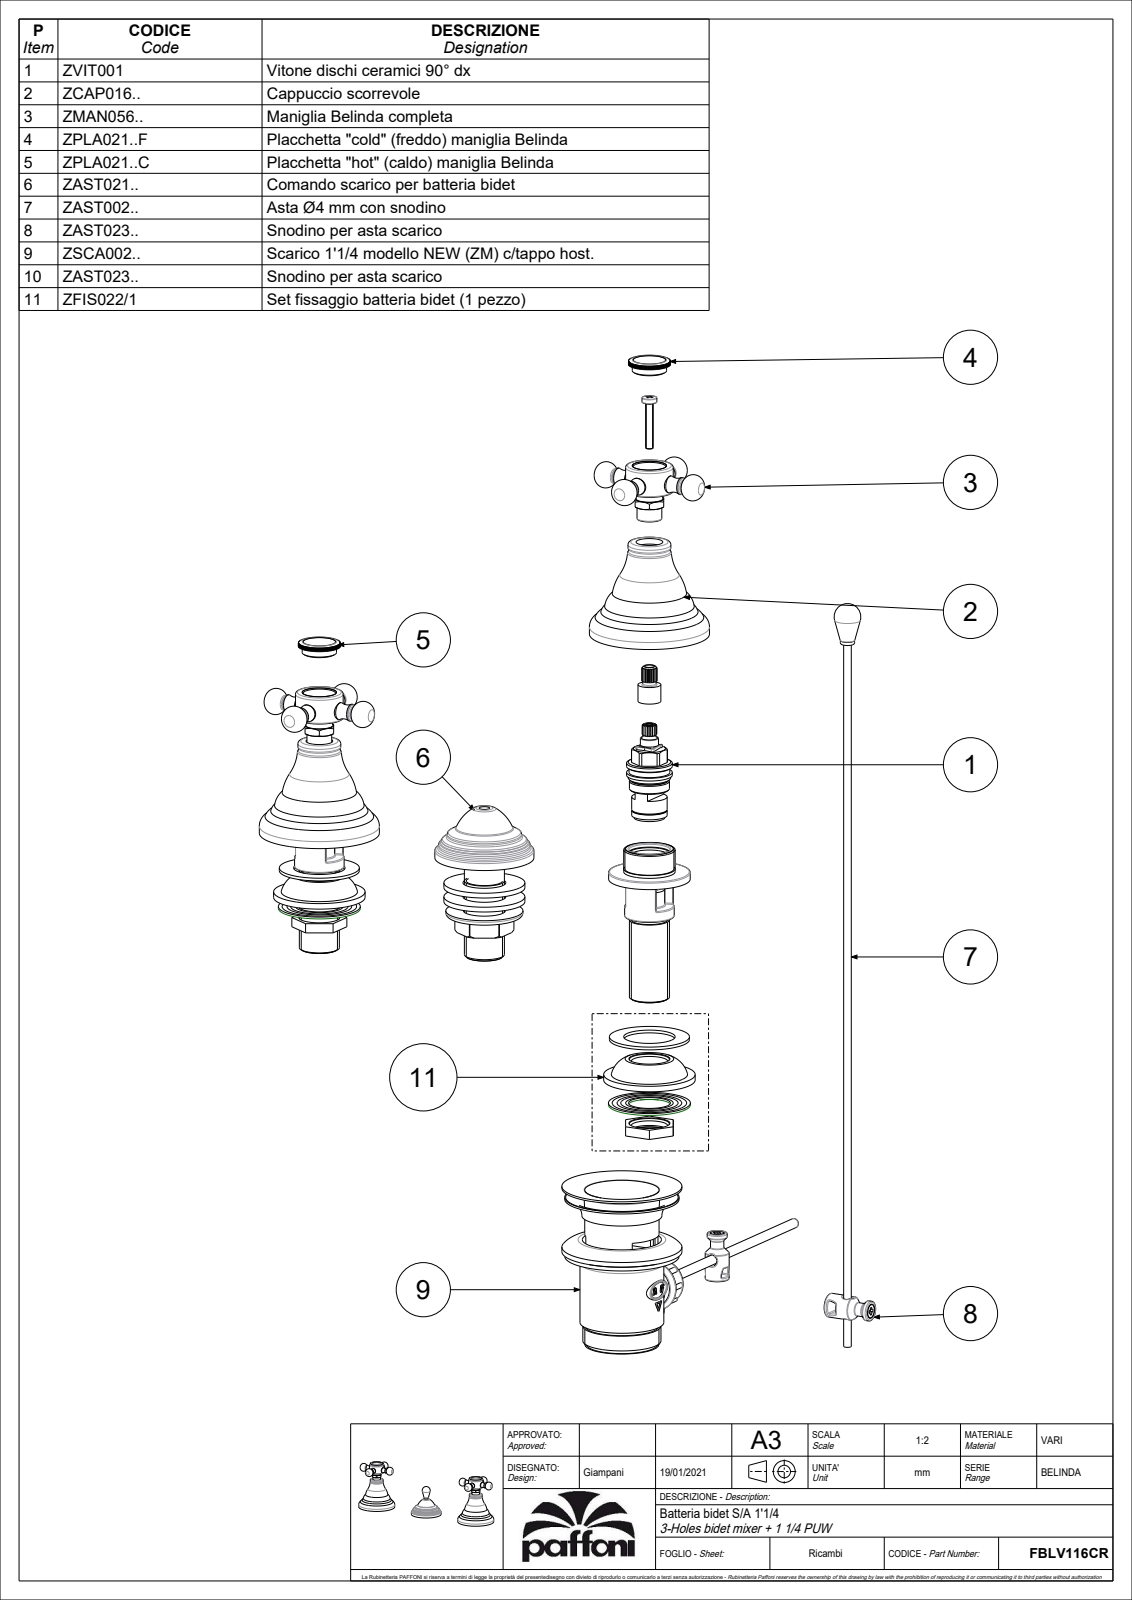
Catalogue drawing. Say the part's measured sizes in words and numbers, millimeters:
The part is named "FBLV116CR". Its 3-D file was written by "CREO PARAMETRIC BY PTC INC, 2020044 (CONFIG_CONTROL_DESIGN)". It is 4 solids with 934 faces: 438 planar, 284 cylindrical and 212 other. Overall it measures 264.07 by 79.2 by 64.07 millimeters. Its volume is 204 286 cubic millimeters and its surface area 39 030 square millimeters. Round holes: 1 of diameter 5.5. Round bosses or shafts: 3 of diameter 9, 3 of diameter 7, 2 of diameter 63, 2 of diameter 25, 2 of diameter 22.5, 2 of diameter 14, 2 of diameter 13, 1 of diameter 52. Partial cylindrical surfaces (rounded edges, fillets, slot ends): 2 of radius 11. The main face-to-face distances are 62.5, 50, 12.5, 15, 15.2, 173.2, 4, 54.5, 4.5, 8.
